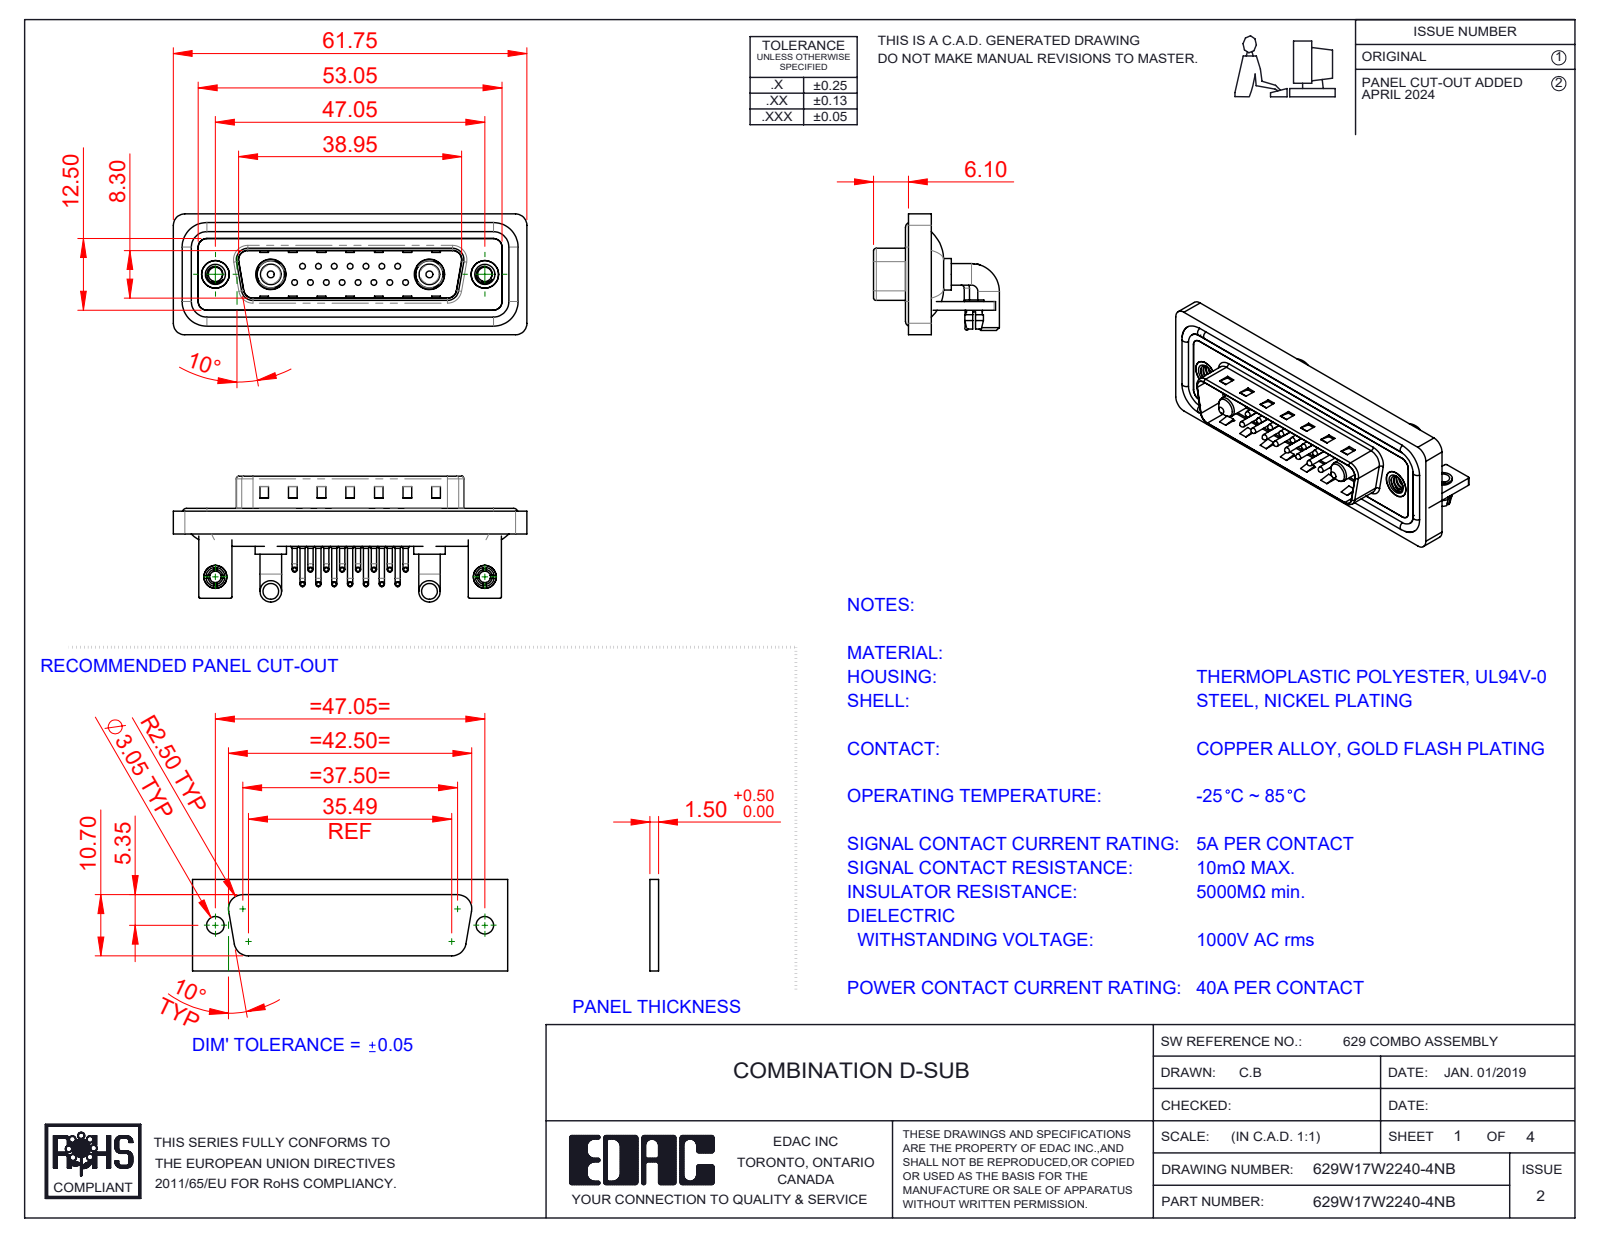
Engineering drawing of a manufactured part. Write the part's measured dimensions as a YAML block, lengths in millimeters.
part_name: "629Combo Threaded Rivet_B; 629Combo Board Lock; 629Combo Shell Rear_25 Contacts; 629W17W2240-4NB (+7 more)"
step_written_by: "SolidWorks 2023 (CONFIG_CONTROL_DESIGN)"
units: millimeters
bodies: {solids: 30, faces: 2349, planar: 1257, cylindrical: 820, other: 272}
overall_size: [61.75, 21.98, 21.1]
volume: 7966
surface_area: 13487
round_holes:
  - {diameter: 2, count: 17}
  - {diameter: 0.75, count: 15}
  - {diameter: 1.6, count: 15}
  - {diameter: 2.5, count: 4}
  - {diameter: 3.2, count: 2}
  - {diameter: 4, count: 2}
  - {diameter: 4.8, count: 2}
  - {diameter: 4.85, count: 2}
  - {diameter: 5, count: 2}
  - {diameter: 5.3, count: 2}
round_bosses_or_shafts:
  - {diameter: 0.9, count: 30}
  - {diameter: 1.5, count: 15}
  - {diameter: 1, count: 15}
  - {diameter: 0.65, count: 15}
  - {diameter: 3.75, count: 4}
  - {diameter: 1.6, count: 4}
  - {diameter: 5.5, count: 2}
  - {diameter: 5.2, count: 2}
partial_cylinders:
  - {radius: 2, count: 19}
  - {radius: 1.5, count: 18}
  - {radius: 0.25, count: 16}
  - {radius: 1.01, count: 15}
  - {radius: 0.5, count: 9}
  - {radius: 1.6, count: 8}
  - {radius: 0.6, count: 4}
  - {radius: 0.65, count: 4}
face_to_face_distances: [0.4, 0.8, 2.1, 1.5, 2.9, 1.1, 4.1, 1.6, 4.5, 3.7]
hole_center_spacings: [3.16, 2.77, 5.54, 8.31, 5.04, 7.49, 11.08, 5.03]
